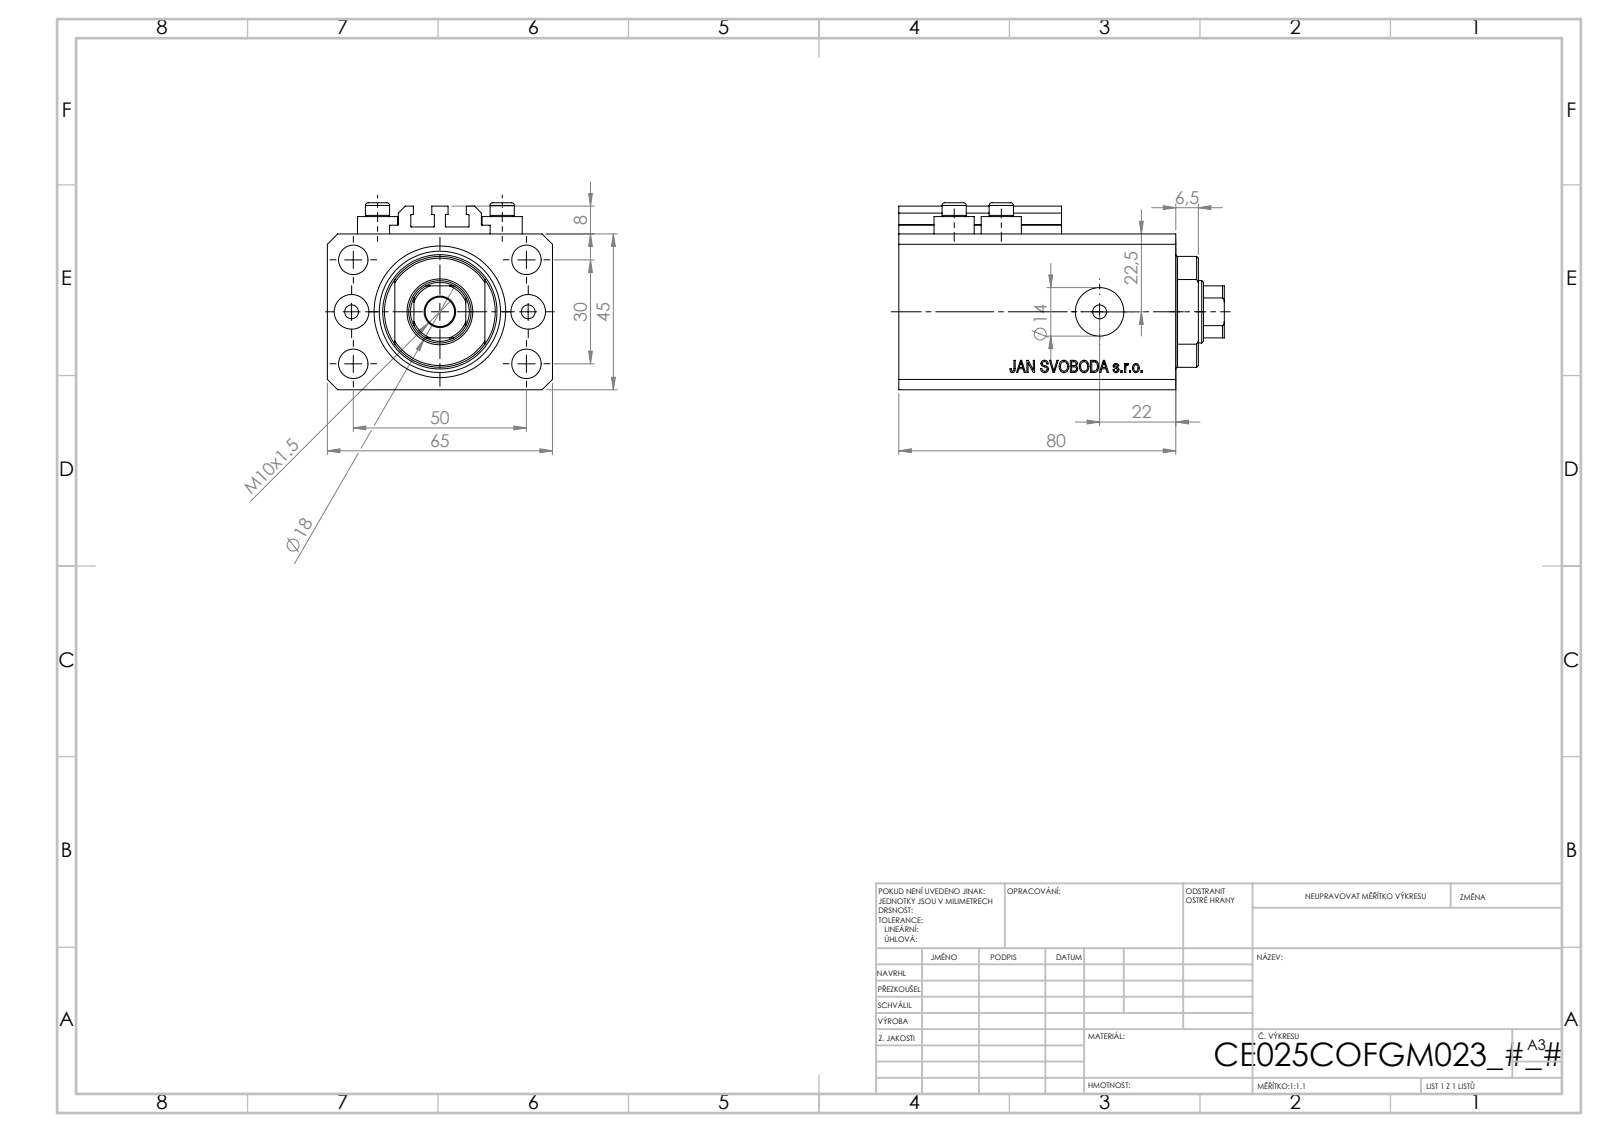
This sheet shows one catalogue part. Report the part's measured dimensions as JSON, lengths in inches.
{"part_name": "ALLEN BOLT V250CE; V250CE_C_Body; V250CE_C_VCP; V250CE_VC_C", "step_written_by": "SolidWorks 2019 (CONFIG_CONTROL_DESIGN)", "units": "inches", "bodies": {"solids": 8, "faces": 1034, "planar": 504, "cylindrical": 86, "other": 444}, "overall_size": [3.701, 2.559, 2.126], "volume_in3": 13.4, "surface_area_in2": 91.35, "round_holes": [[0.157, 8], [0.335, 5], [0.394, 2], [0.551, 2], [0.709, 1], [0.984, 1], [1.496, 1]], "round_bosses_or_shafts": [[0.457, 4], [0.276, 4]], "partial_cylinders_radius": [[0.008, 10], [0.335, 1], [0.63, 1]], "face_to_face_distances": [1.772, 2.559, 0.551, 2.598, 3.15, 1.85, 0.272, 2.327, 2.878, 0.118], "hole_center_spacings": [0.591, 1.148, 2.074, 1.417, 0.535, 1.004, 1.181, 1.515]}
